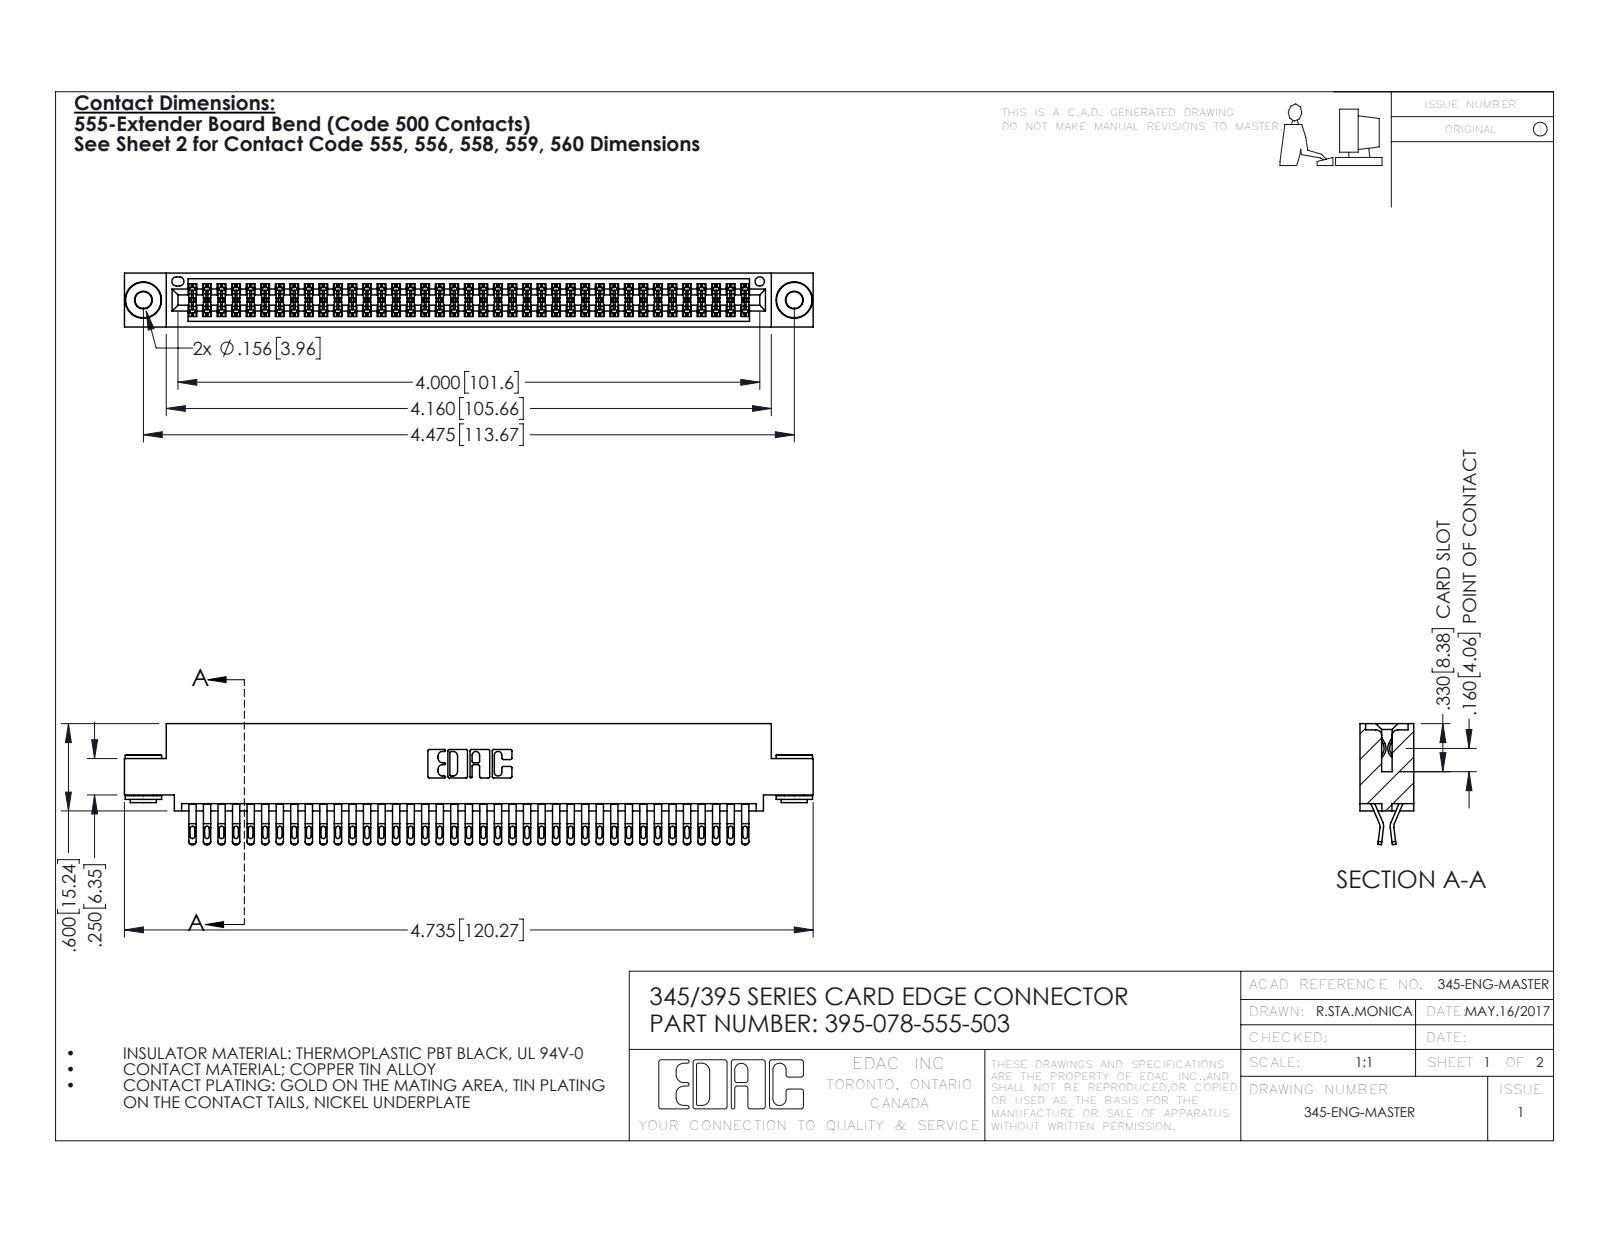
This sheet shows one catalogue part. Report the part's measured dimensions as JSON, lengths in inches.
{"part_name": "345 Part_0.110 Offset - 0.156 Dia-TH; 345-250-002_345-250-002-102; 345-292-001_555 Tail; 395-078-555-503", "step_written_by": "SolidWorks 2016 (CONFIG_CONTROL_DESIGN)", "units": "inches", "bodies": {"solids": 81, "faces": 4536, "planar": 2512, "cylindrical": 2016, "other": 8}, "overall_size": [4.735, 0.832, 0.37], "volume_in3": 0.722, "surface_area_in2": 28.69, "round_holes": [[0.116, 2], [0.156, 2], [0.064, 1]], "round_bosses_or_shafts": [[0.25, 2], [0.18, 2], [0.136, 2]], "partial_cylinders_radius": [[0.016, 195], [0.02, 156], [0.006, 117], [0.01, 22], [0.007, 6], [0.031, 6], [0.026, 3], [0.01, 2]], "face_to_face_distances": [0.072, 0.298, 0.025, 0.37, 0.2, 0.098, 0.272, 0.225, 0.175, 0.149], "hole_center_spacings": [0.27, 4.239, 4.475]}
